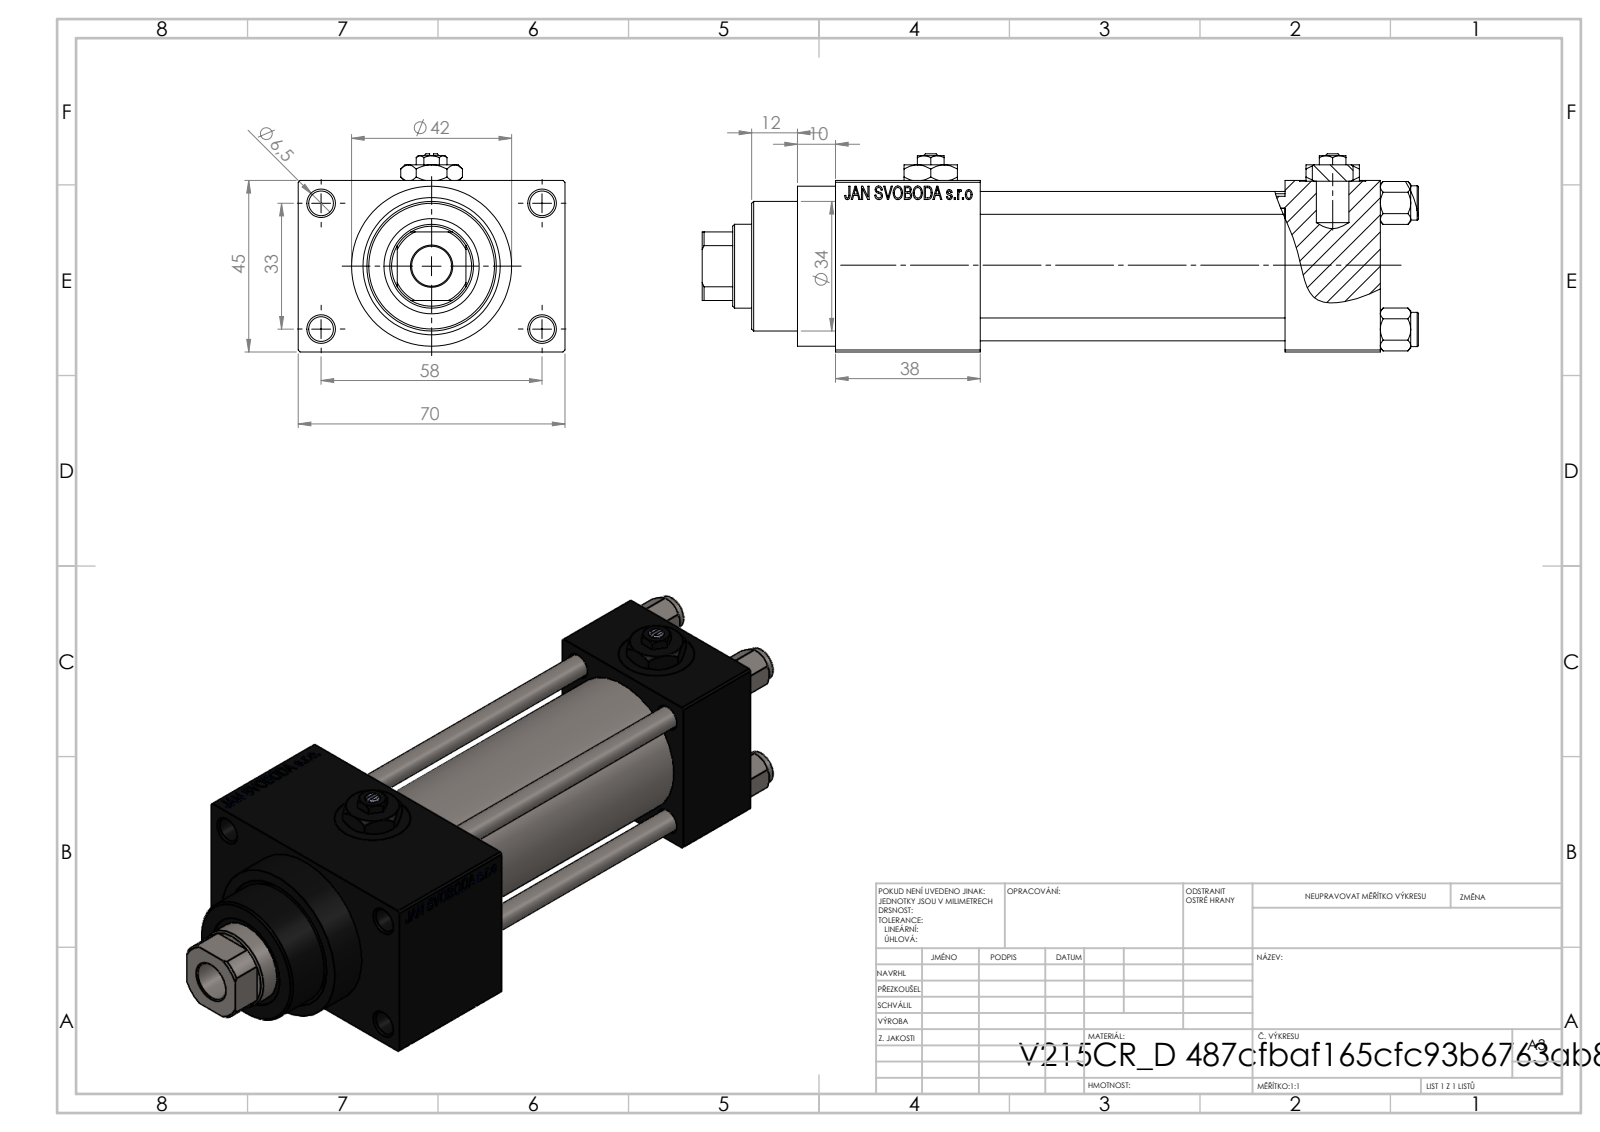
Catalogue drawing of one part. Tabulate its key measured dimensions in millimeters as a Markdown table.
| quantity | value |
| --- | --- |
| part name | NUT_M5_D; V215_VC_A; V215CR_D_Body; V215CR_VCP_D (+2 more) |
| STEP written by | SolidWorks 2019 (CONFIG_CONTROL_DESIGN) |
| units | millimeters |
| bodies | 13 solids, 1203 faces (542 planar, 99 cylindrical, 562 other) |
| overall size | 188 × 70 × 52 |
| volume | 266 318 mm³ |
| surface area | 92 557 mm² |
| round holes (diameter × count) | 6 × 4, 6.5 × 4, 13.16 × 4, 20 × 4, 7 × 3, 10.5 × 1, 22 × 1, 24 × 1, 25 × 1, 32 × 1, 33 × 1 |
| round bosses / shafts (diameter × count) | 9 × 4, 42 × 1, 38 × 1, 34 × 1 |
| partial cylindrical surfaces (radius × count) | 10.5 × 1 |
| main face-to-face distances | 45, 25, 12.5, 80, 105, 57.5, 118, 38, 143, 70 |
| hole center spacings | 12.4, 23.48, 33.2, 33.37, 35.35, 45.6, 56.35, 33 |
